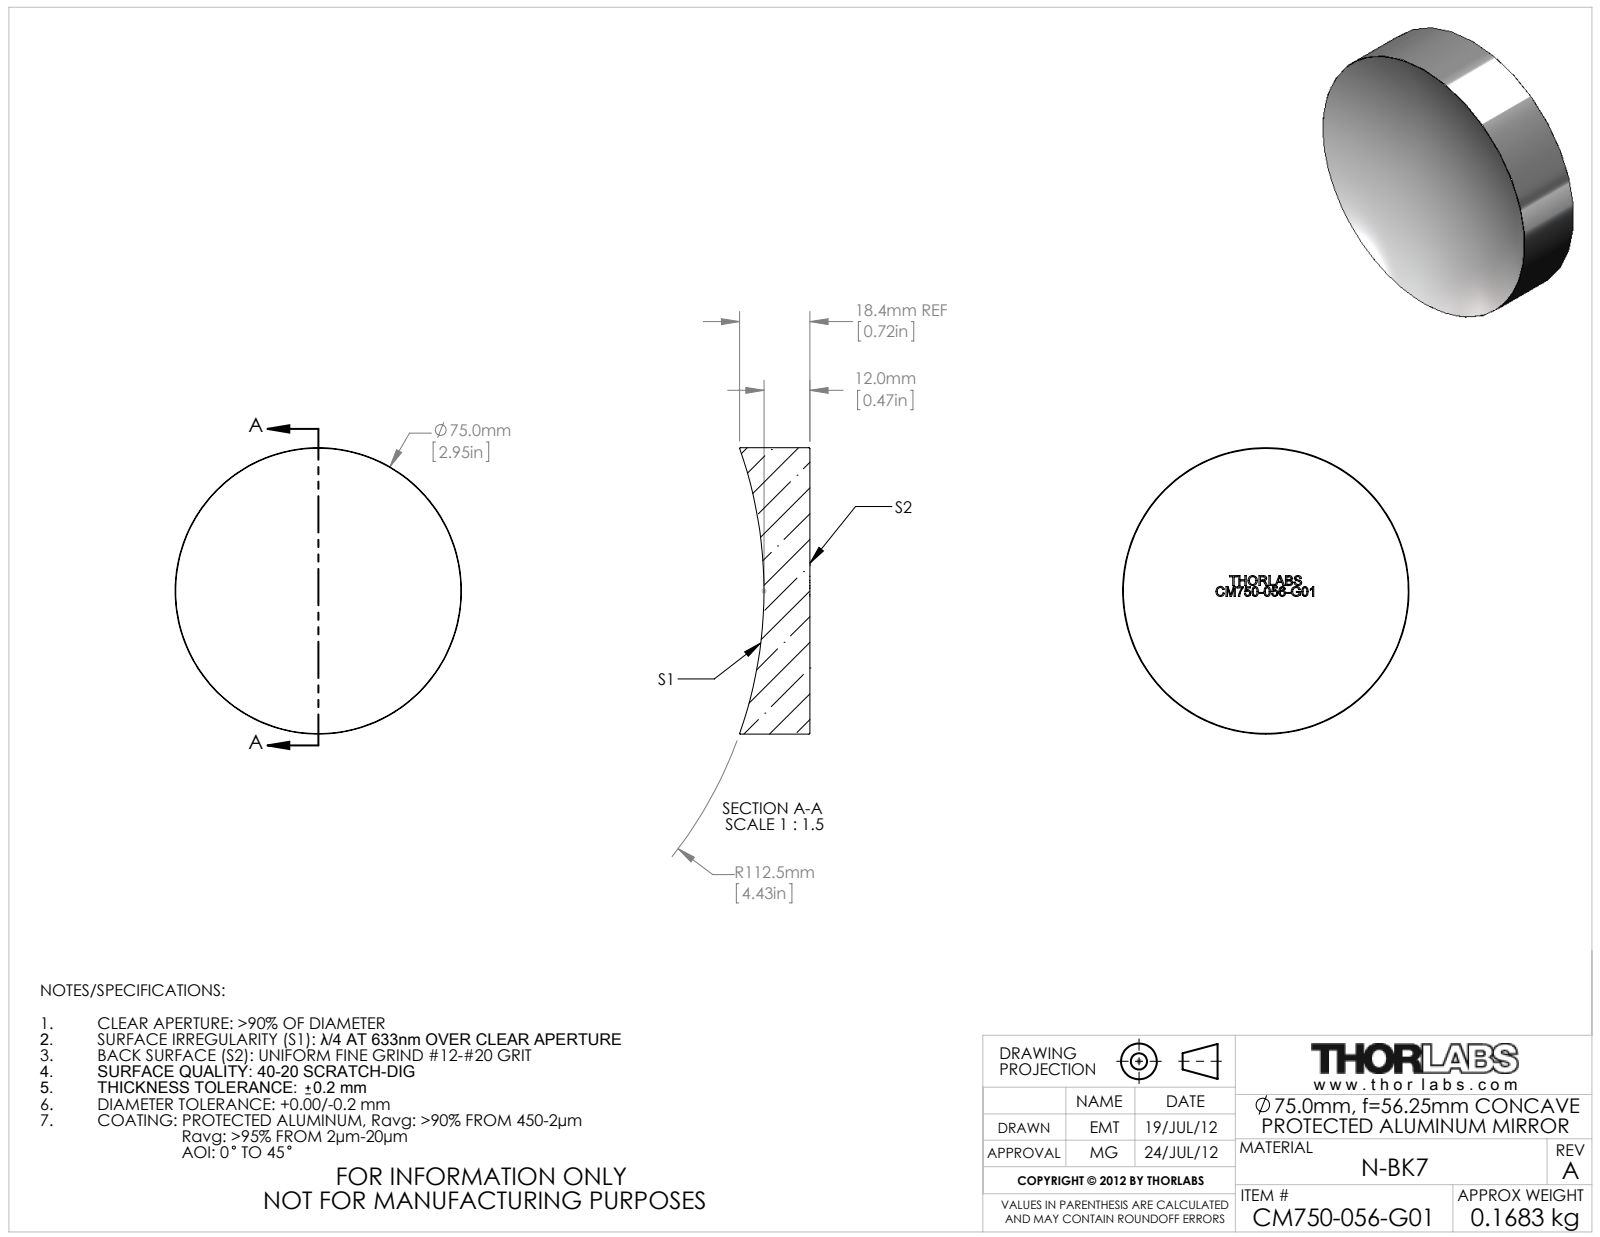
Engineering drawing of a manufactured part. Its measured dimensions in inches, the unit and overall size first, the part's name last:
Units: inches
Overall size (bounding box): 2.953 × 2.953 × 0.724
Round bosses / shafts (diameter × count): ⌀2.953 ×1
Bodies: 0 solids, 39 faces (31 planar, 2 cylindrical, 6 other)
Part name (STEP PRODUCT): 24638-E0W
STEP written by: SolidWorks 2011 (CONFIG_CONTROL_DESIGN)
